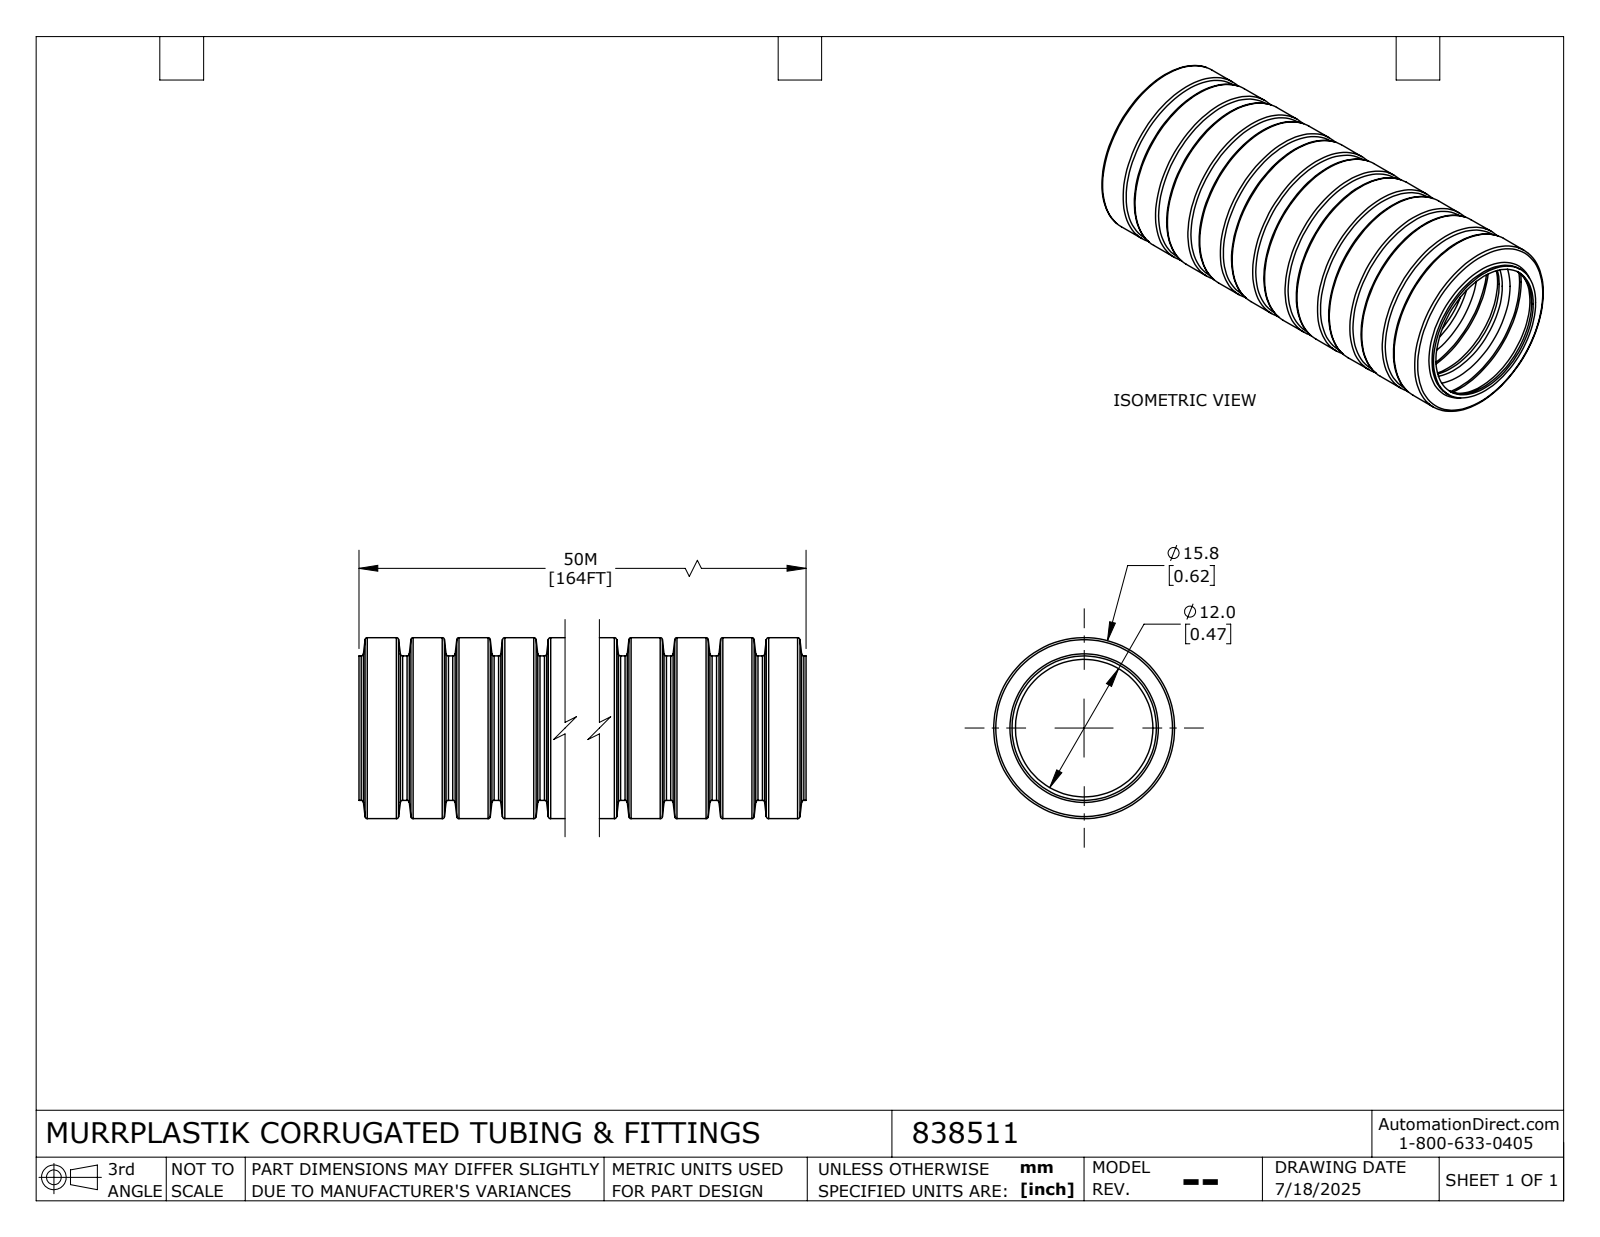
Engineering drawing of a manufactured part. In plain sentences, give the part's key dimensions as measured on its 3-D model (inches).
The part is named "838511_Default". Its 3-D file was written by "SolidWorks 2024 (CONFIG_CONTROL_DESIGN)". It is 1 solid with 164 faces: 2 planar, 42 cylindrical and 120 other. Overall it measures 1.575 by 0.622 by 0.622 inches. Its volume is 0.055 cubic inches and its surface area 9.139 square inches. Round holes: 1 of diameter 0.472, 1 of diameter 0.598. Round bosses or shafts: 1 of diameter 0.622, 1 of diameter 0.496. The main face-to-face distances are 1.575.
